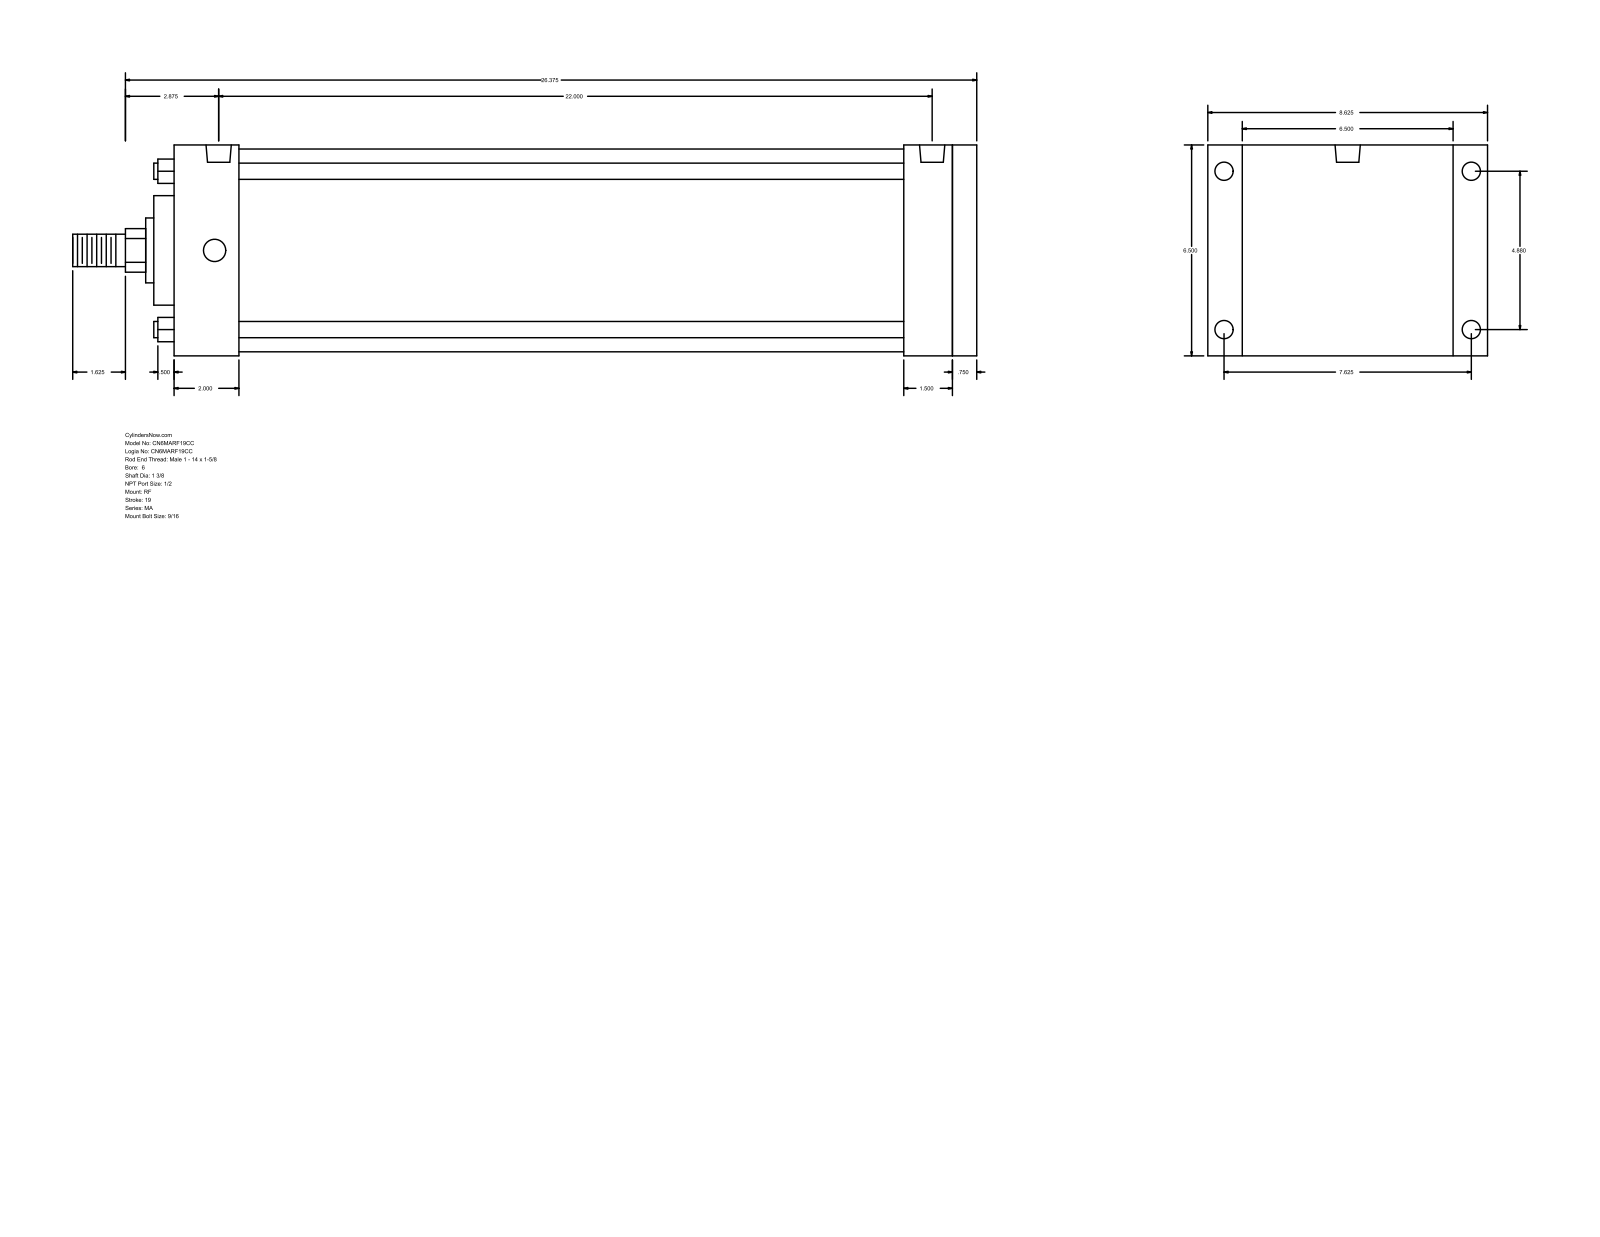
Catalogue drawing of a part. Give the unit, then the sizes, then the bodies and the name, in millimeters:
Units: millimetres
Overall size (bounding box): 711.2 × 219.07 × 165.1
Round holes (diameter × count): ⌀14.29 ×4, ⌀17.46 ×4, ⌀19.77 ×2
Round bosses / shafts (diameter × count): ⌀12.7 ×4, ⌀158.75 ×1, ⌀85.72 ×1, ⌀50.8 ×1, ⌀34.92 ×1, ⌀25.4 ×1
Partial cylindrical surfaces — rounded edges, fillets, slot ends (radius × count): R17.06 ×1
Main face-to-face distances: 165.1, 631.82, 612.78, 19.04, 57.15, 50.8, 561.98, 581.02, 574.67, 523.87
Hole centre spacings: 123.96, 193.68, 229.95, 561.98, 3.18, 558.8
Bodies: 0 solids, 94 faces (65 planar, 29 cylindrical, 0 other)
Part name (STEP PRODUCT): MA_RF__0600_1.375
STEP written by: GSSL Pune (CONFIG_CONTROL_DESIGN)
